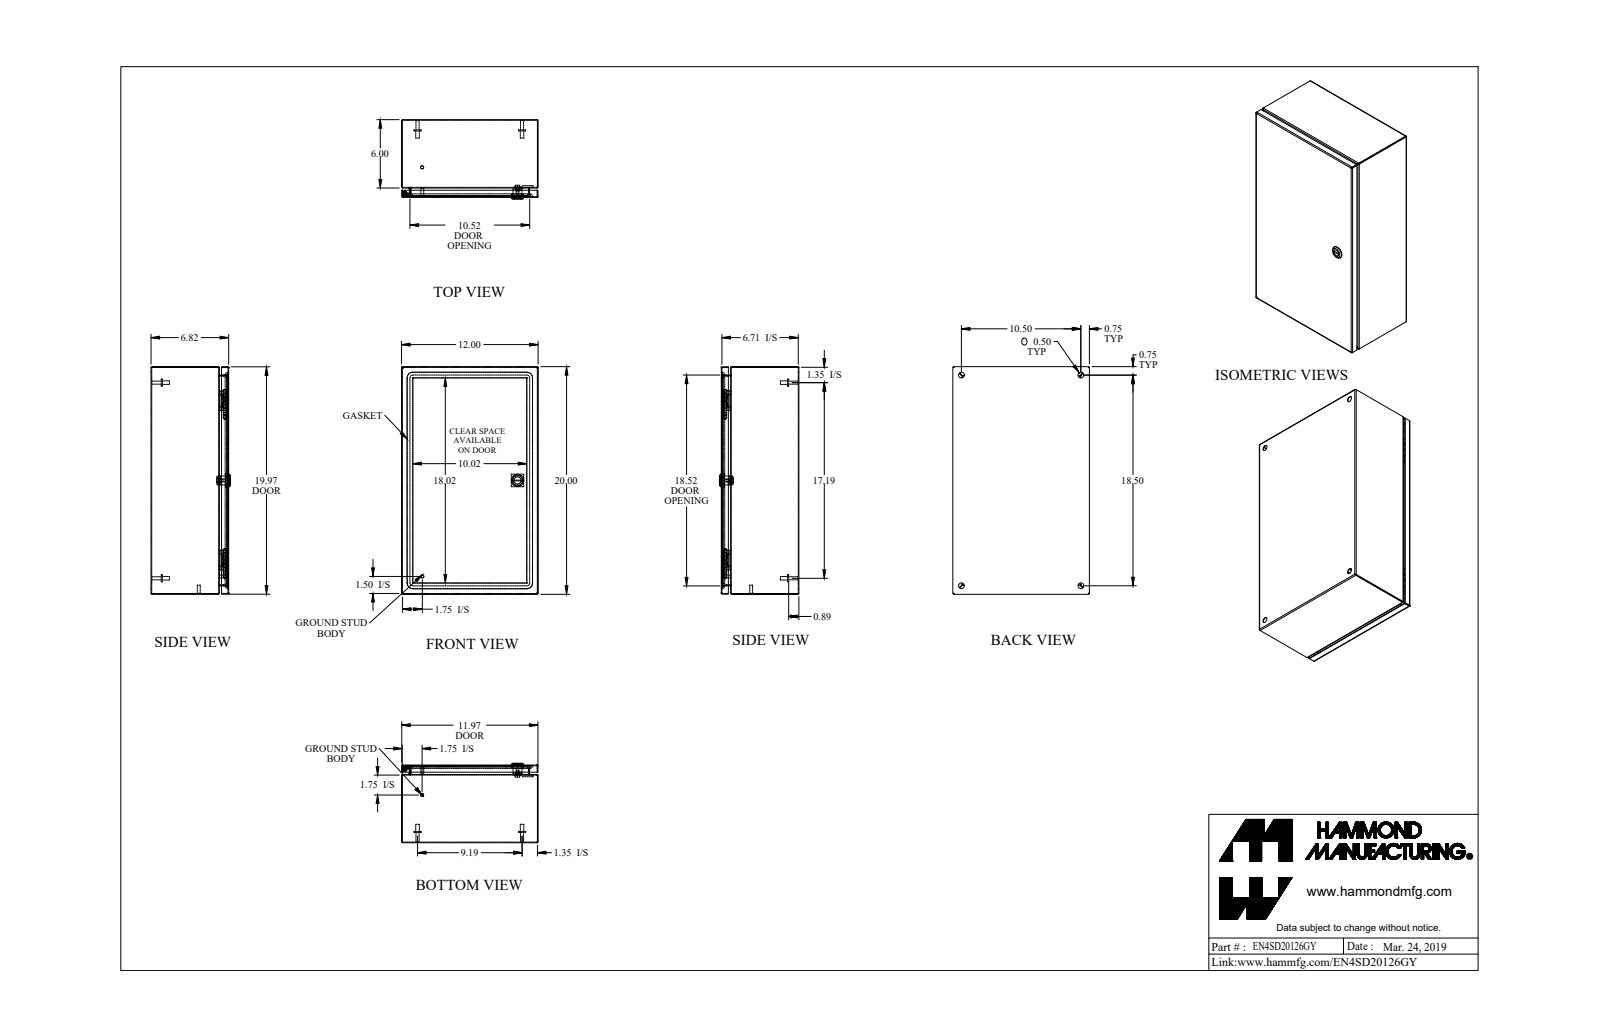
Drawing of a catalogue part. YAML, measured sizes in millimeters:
part_name: "EN4SD20126GY_Default"
step_written_by: "SolidWorks 2019 (CONFIG_CONTROL_DESIGN)"
units: millimeters
bodies: {solids: 21, faces: 634, planar: 285, cylindrical: 213, other: 136}
overall_size: [508, 304.8, 177.3]
volume: 1030000
surface_area: 1368000
round_holes:
  - {diameter: 12.7, count: 4}
  - {diameter: 4.4, count: 1}
  - {diameter: 5.9, count: 1}
  - {diameter: 6.1, count: 1}
  - {diameter: 6.1, count: 1}
  - {diameter: 15.9, count: 1}
  - {diameter: 19.9, count: 1}
round_bosses_or_shafts:
  - {diameter: 15.9, count: 4}
  - {diameter: 8, count: 4}
  - {diameter: 6.9, count: 4}
  - {diameter: 7.1, count: 2}
  - {diameter: 6.4, count: 2}
  - {diameter: 27.9, count: 1}
  - {diameter: 13.3, count: 1}
  - {diameter: 11.6, count: 1}
partial_cylinders:
  - {radius: 0.7, count: 21}
  - {radius: 2.2, count: 21}
  - {radius: 6.4, count: 16}
  - {radius: 482.6, count: 8}
  - {radius: 0.2, count: 4}
  - {radius: 1.6, count: 4}
  - {radius: 12.7, count: 4}
  - {radius: 3.2, count: 2}
face_to_face_distances: [1.4, 171.8, 170.4, 173.3, 303.4, 506.6, 301.9, 304.8, 20.9, 151]
hole_center_spacings: [266.7, 469.9, 540.3, 236.5, 236.5, 335.7, 335.7]
